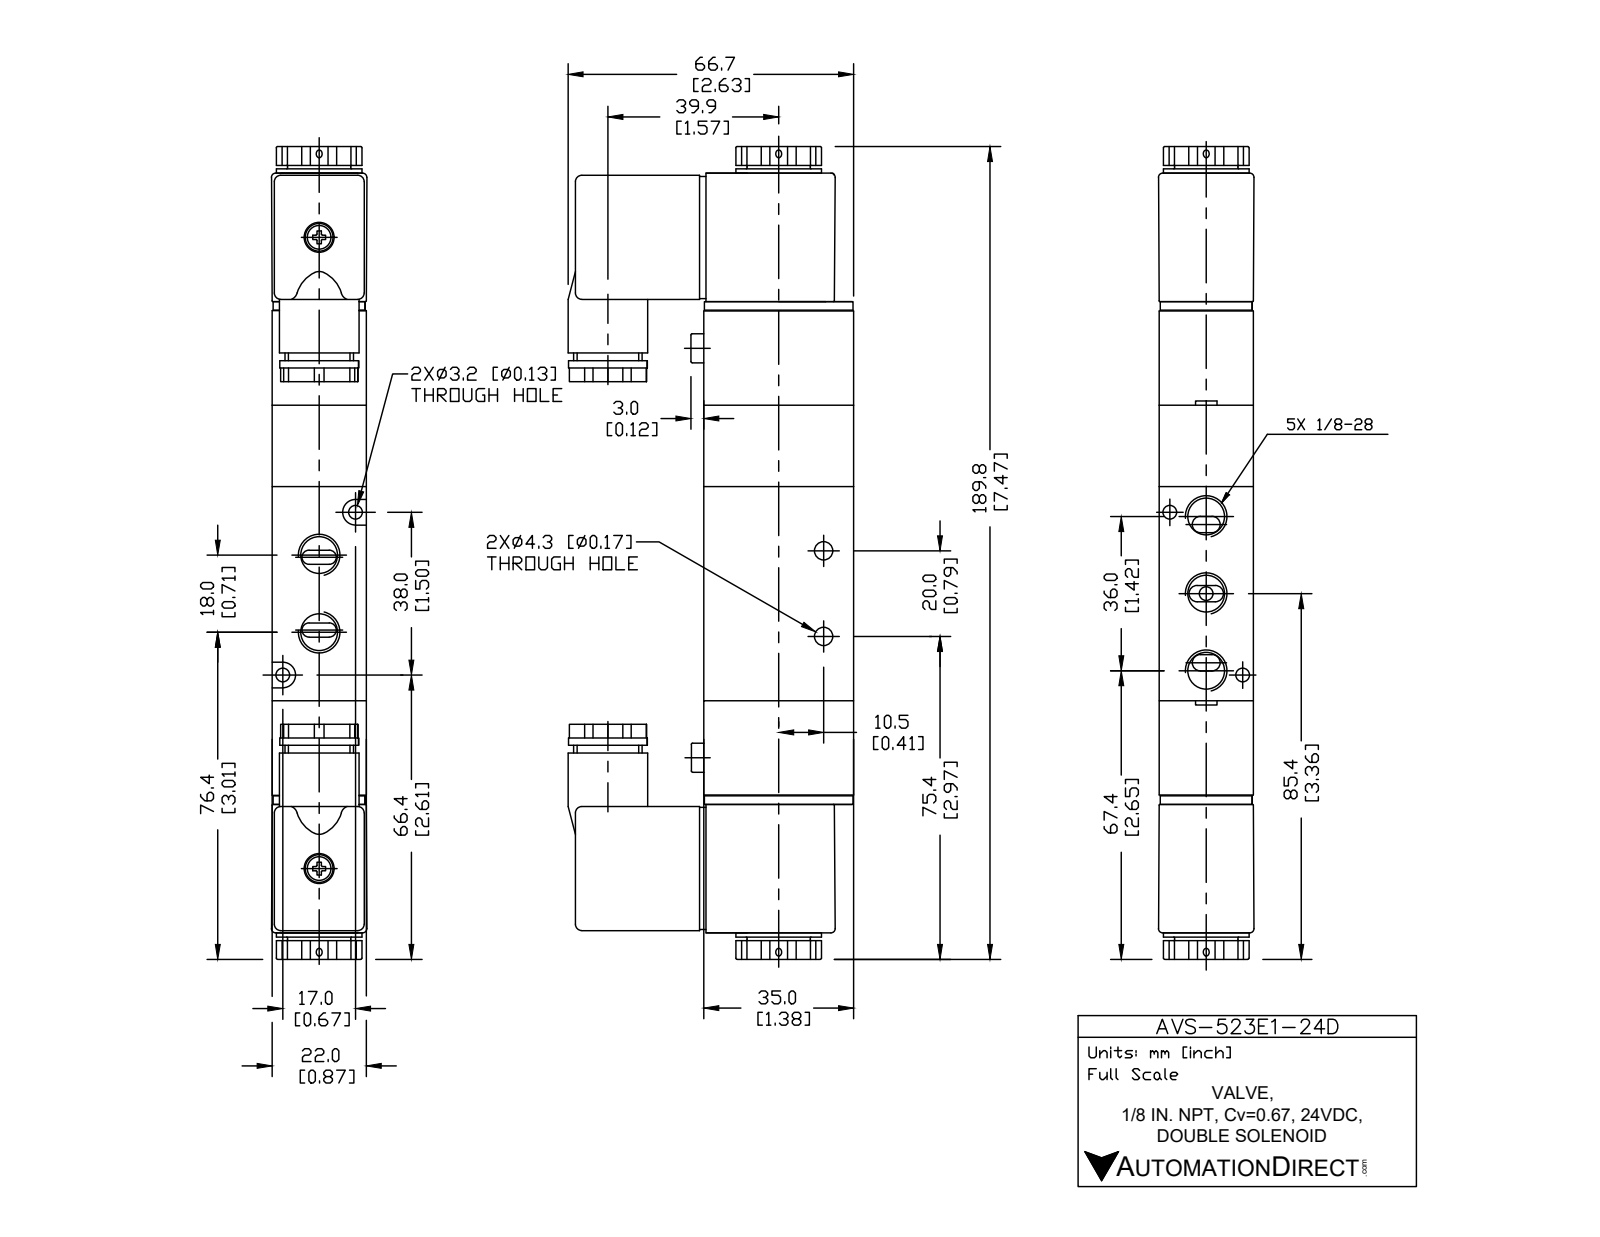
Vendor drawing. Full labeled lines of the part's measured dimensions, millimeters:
Part name (STEP PRODUCT): AVS-523E1-24D
STEP written by: SolidWorks 2015 (CONFIG_CONTROL_DESIGN)
Units: millimetres
Bodies: 5 solids, 236 faces (129 planar, 91 cylindrical, 16 other)
Overall size (bounding box): 189.82 × 66.7 × 22
Volume: 150 497 mm³ · Surface area: 37 557 mm²
Round holes (diameter × count): ⌀8.43 ×5, ⌀3.2 ×2, ⌀4.3 ×2, ⌀9.3 ×1
Round bosses / shafts (diameter × count): ⌀6.8 ×2, ⌀18.6 ×1, ⌀17.6 ×1, ⌀15.81 ×1, ⌀13.02 ×1, ⌀11 ×1
Partial cylindrical surfaces — rounded edges, fillets, slot ends (radius × count): R1.54 ×10, R0.3 ×8, R0.5 ×8, R1 ×8, R3 ×2
Main face-to-face distances: 0.88, 21.74, 1.95, 20.05, 22, 18.1, 22.62, 69, 30.59, 5.03
Hole centre spacings: 8.56, 18, 20.81, 37.96, 7.54, 7.83, 10.53, 10.55
